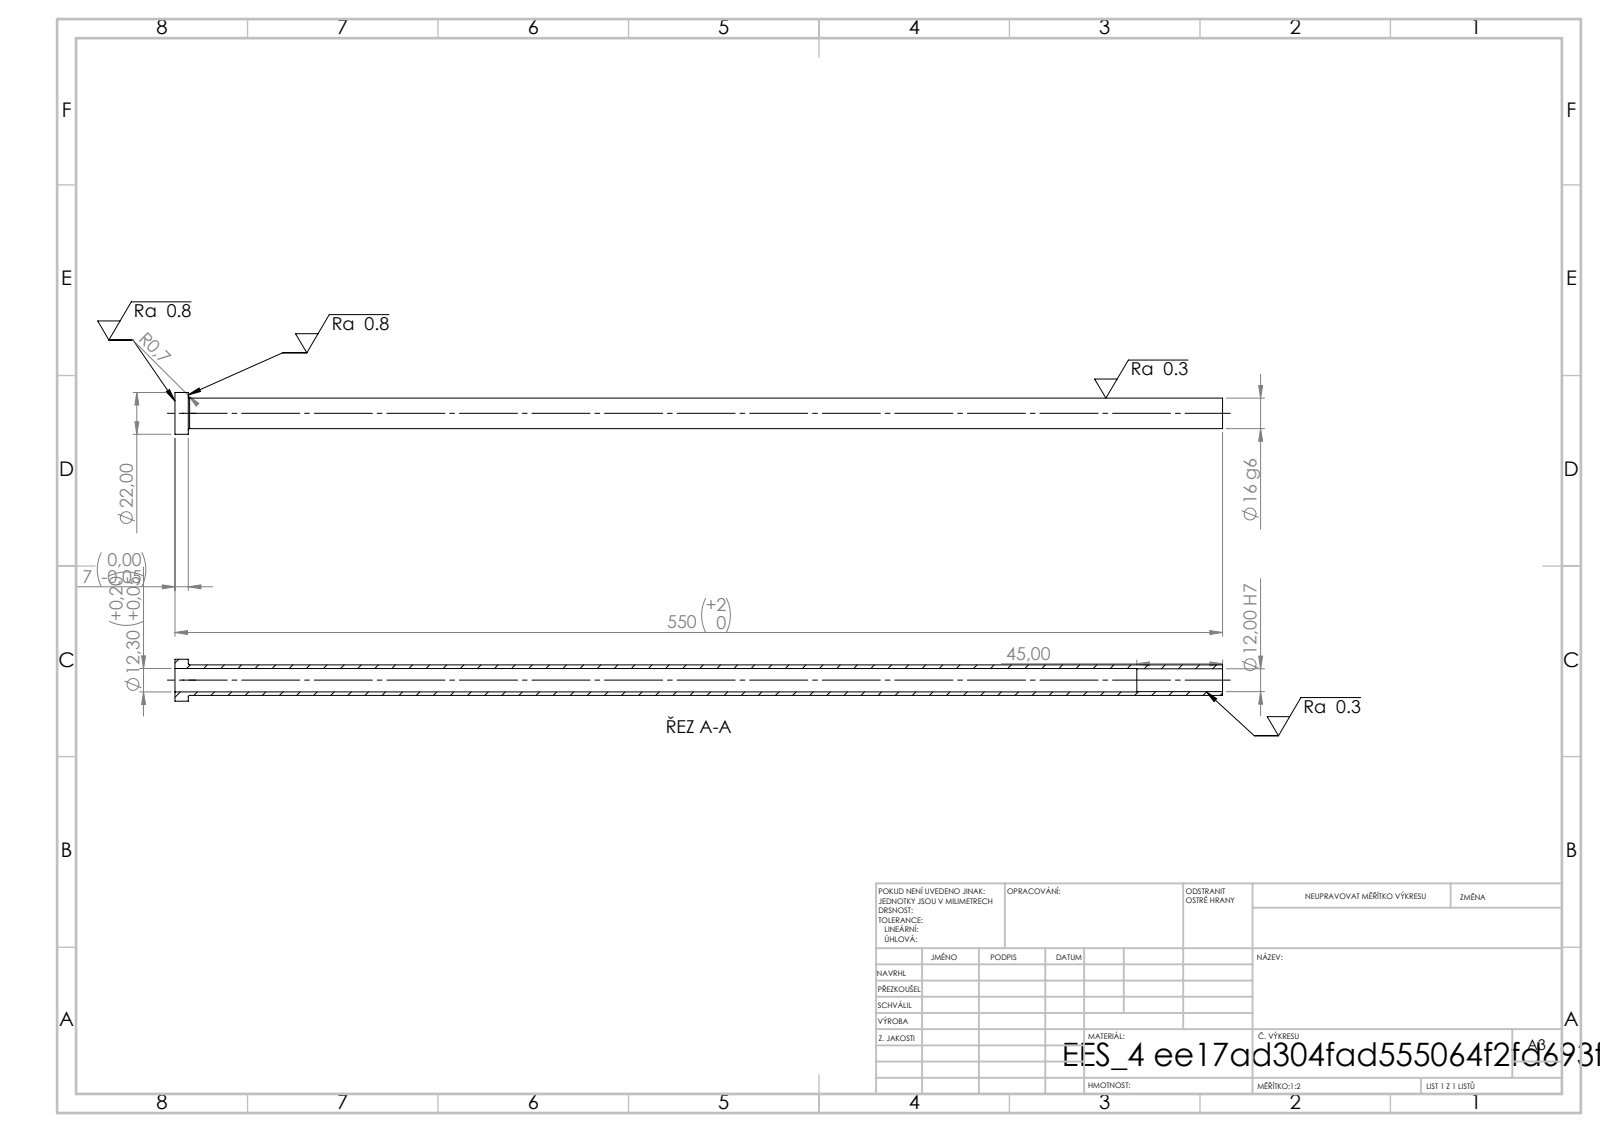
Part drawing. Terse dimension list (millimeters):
written by: SolidWorks 2019 (CONFIG_CONTROL_DESIGN)
unit: mm
bodies: 1 solid, 14 faces (4 planar, 8 cylindrical, 2 other)
size: 550 × 22 × 22
volume: 46 748 mm³; area: 49 508 mm²
holes: 1× ⌀12, 1× ⌀12.3
bosses: 1× ⌀22, 1× ⌀16
face distances: 7, 550, 543, 505, 498, 45
